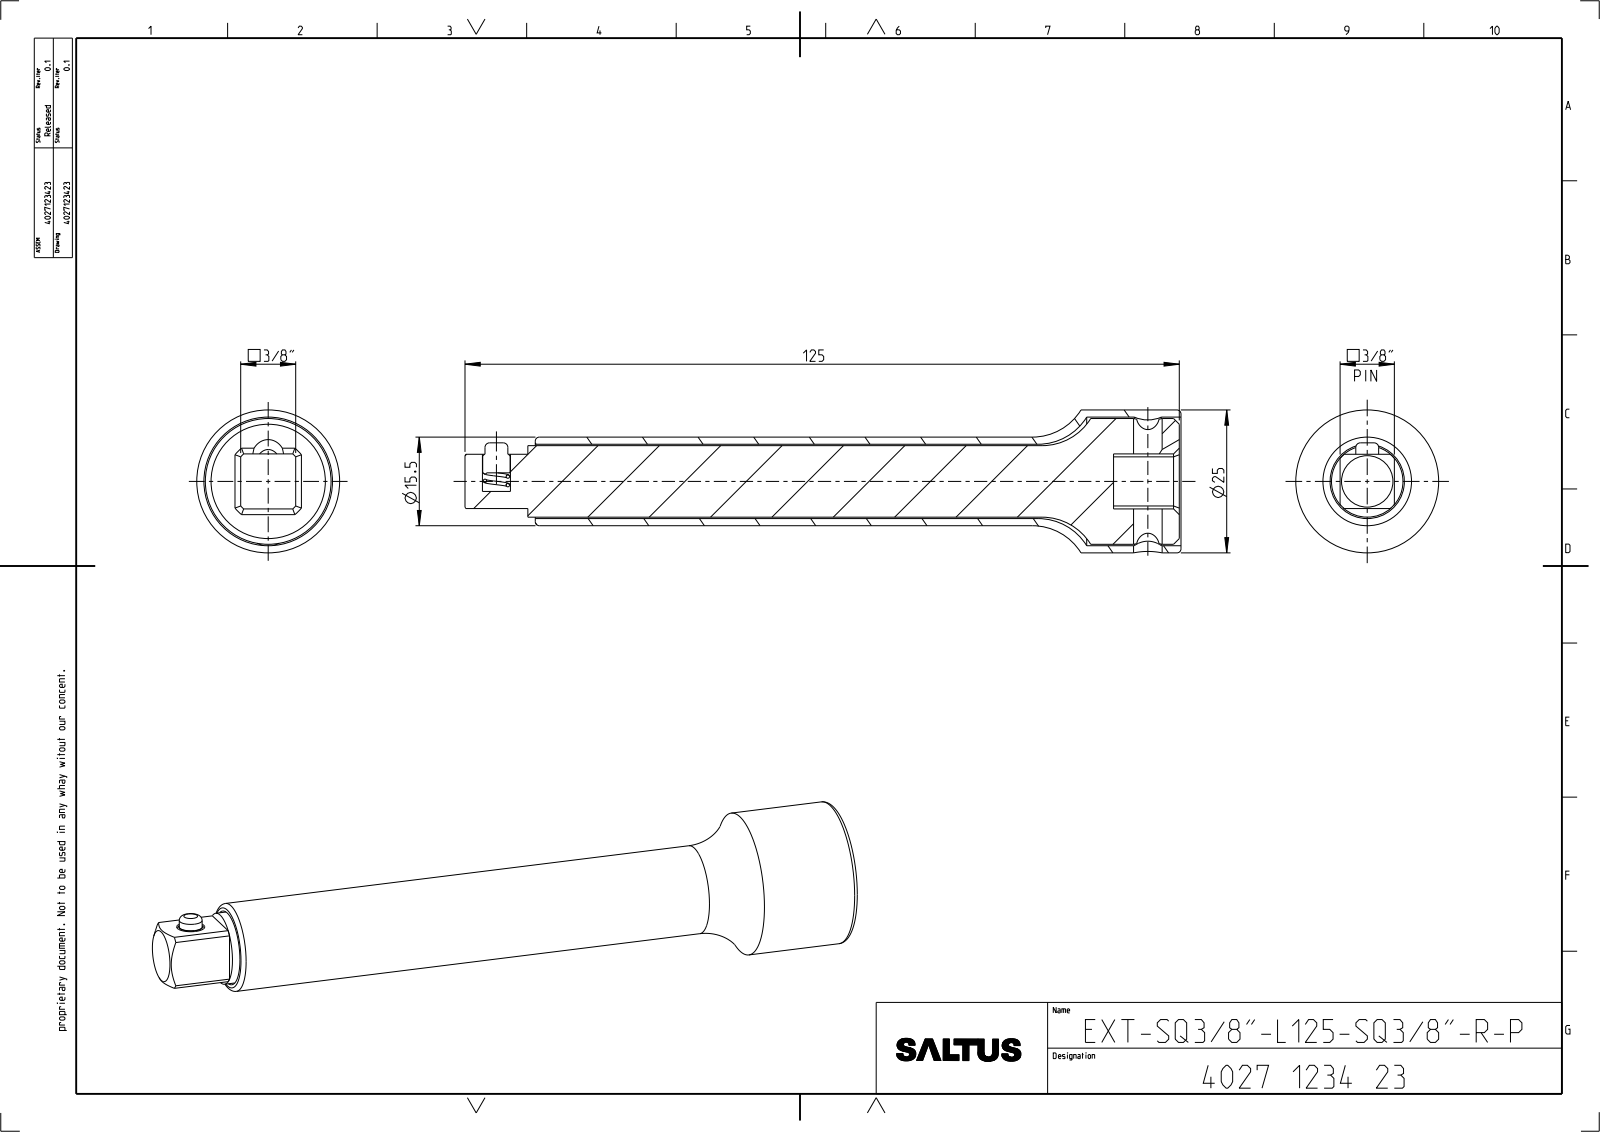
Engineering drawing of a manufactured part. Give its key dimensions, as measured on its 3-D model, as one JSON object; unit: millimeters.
{"part_name": "4027123403; 4027040392; 4027123423_ASM", "step_written_by": "CREO PARAMETRIC BY PTC INC, 2022414 (CONFIG_CONTROL_DESIGN)", "units": "millimeters", "bodies": {"solids": 3, "faces": 88, "planar": 24, "cylindrical": 37, "other": 27}, "overall_size": [125.3, 25, 25], "volume_mm3": 25273, "surface_area_mm2": 18346, "round_holes": [[4.9, 1], [5, 1], [13, 1], [22.5, 1]], "round_bosses_or_shafts": [[25, 1], [22, 1], [15.5, 1], [12.51, 1], [4.8, 1], [4, 1]], "partial_cylinders_radius": [[3, 1], [6.22, 1], [6.45, 1]], "face_to_face_distances": [9.56, 9.5, 9.62, 11.5, 125, 113.5, 11.8, 125.3, 114.3, 114], "hole_center_spacings": [114]}
